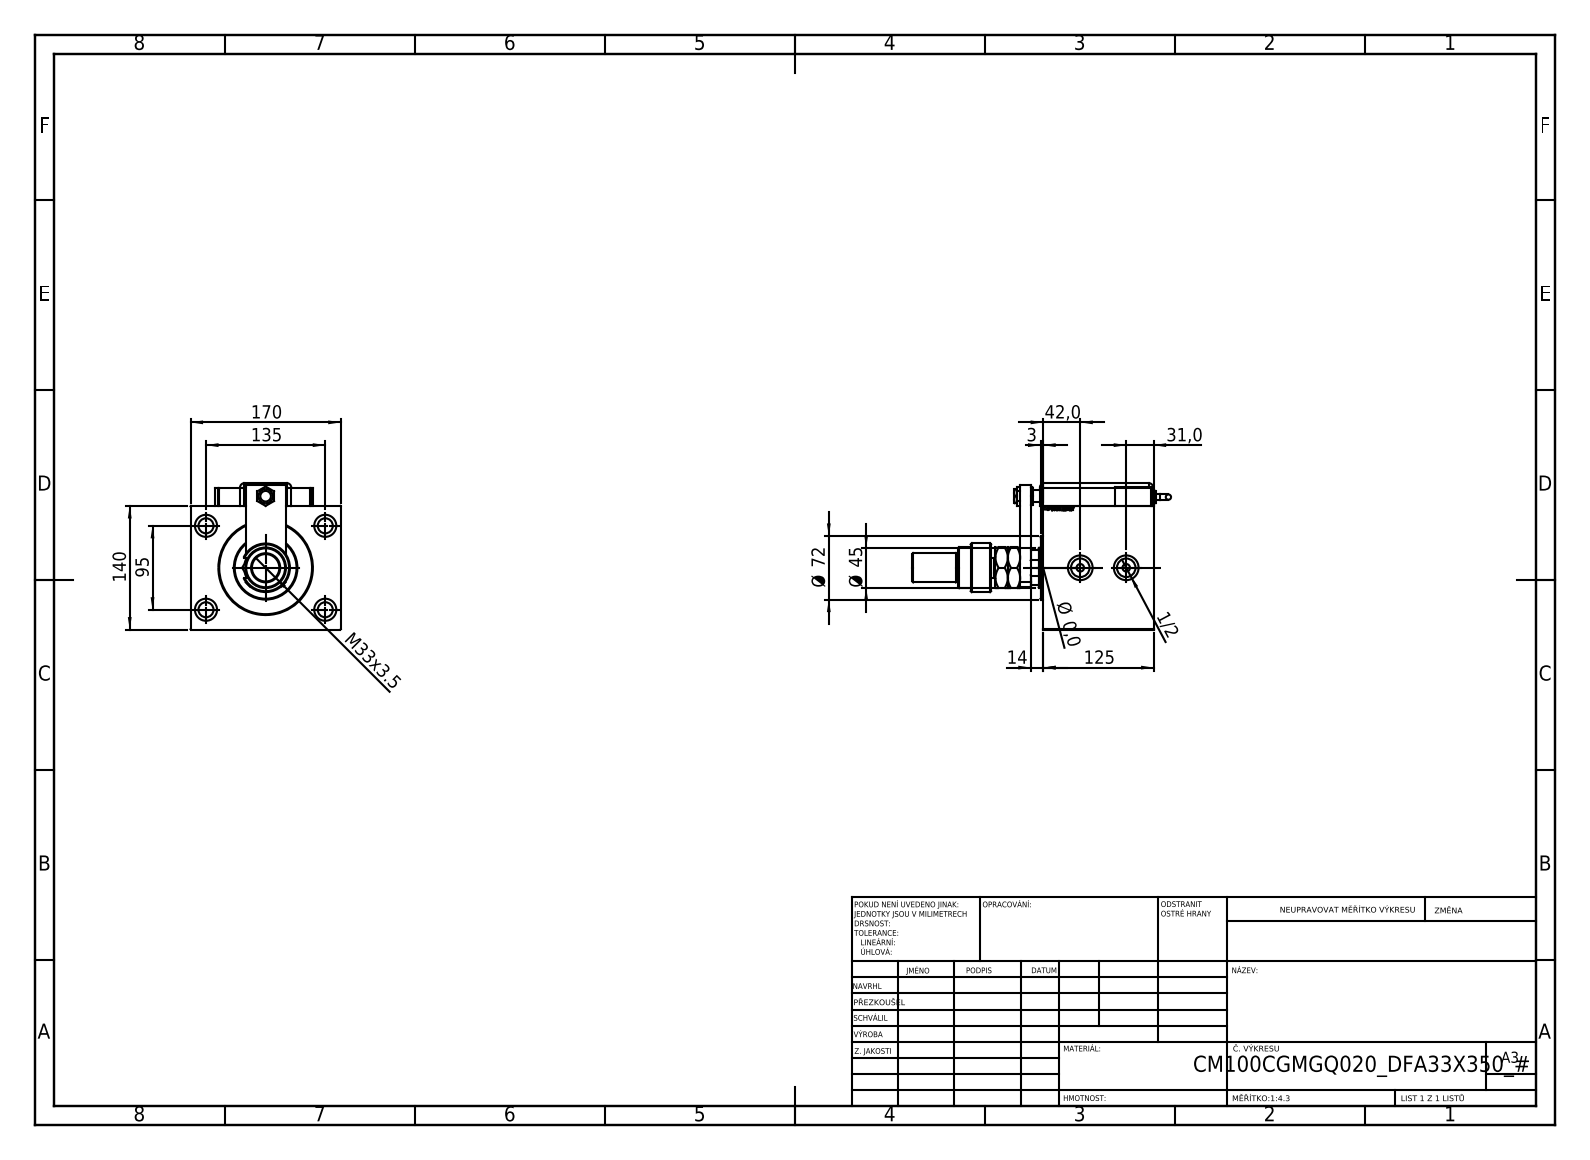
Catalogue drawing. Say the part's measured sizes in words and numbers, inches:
The part is named "FEMALE_PART_FOR_DFA; NUT_D13; MFA; TYC (+8 more)". Its 3-D file was written by "SolidWorks 2019 (CONFIG_CONTROL_DESIGN)". It is 15 solids with 1335 faces: 644 planar, 130 cylindrical and 561 other. Overall it measures 11.526 by 6.693 by 6.528 inches. Its volume is 188.9 cubic inches and its surface area 511.3 square inches. Round holes: 4 of diameter 0.669, 4 of diameter 0.984, 2 of diameter 0.157, 2 of diameter 0.315, 2 of diameter 0.335, 2 of diameter 0.825, 2 of diameter 1.102, 1 of diameter 0.472, 1 of diameter 0.512, 1 of diameter 0.551, 1 of diameter 1.24, 1 of diameter 1.299. Round bosses or shafts: 3 of diameter 0.787, 2 of diameter 0.63, 2 of diameter 0.551, 2 of diameter 0.236, 1 of diameter 2.835, 1 of diameter 2.165, 1 of diameter 1.811, 1 of diameter 1.378. Partial cylindrical surfaces (rounded edges, fillets, slot ends): 9 of radius 0.197, 1 of radius 0.394, 1 of radius 0.453, 1 of radius 0.866. The main face-to-face distances are 5.512, 4.921, 2.008, 6.693, 2.913, 0.118, 0.394, 0.85, 1.157, 4.071. The hole center spacings are 3.25, 2.967, 3.74, 5.315, 5.715, 6.499, 0.787, 2.047.
